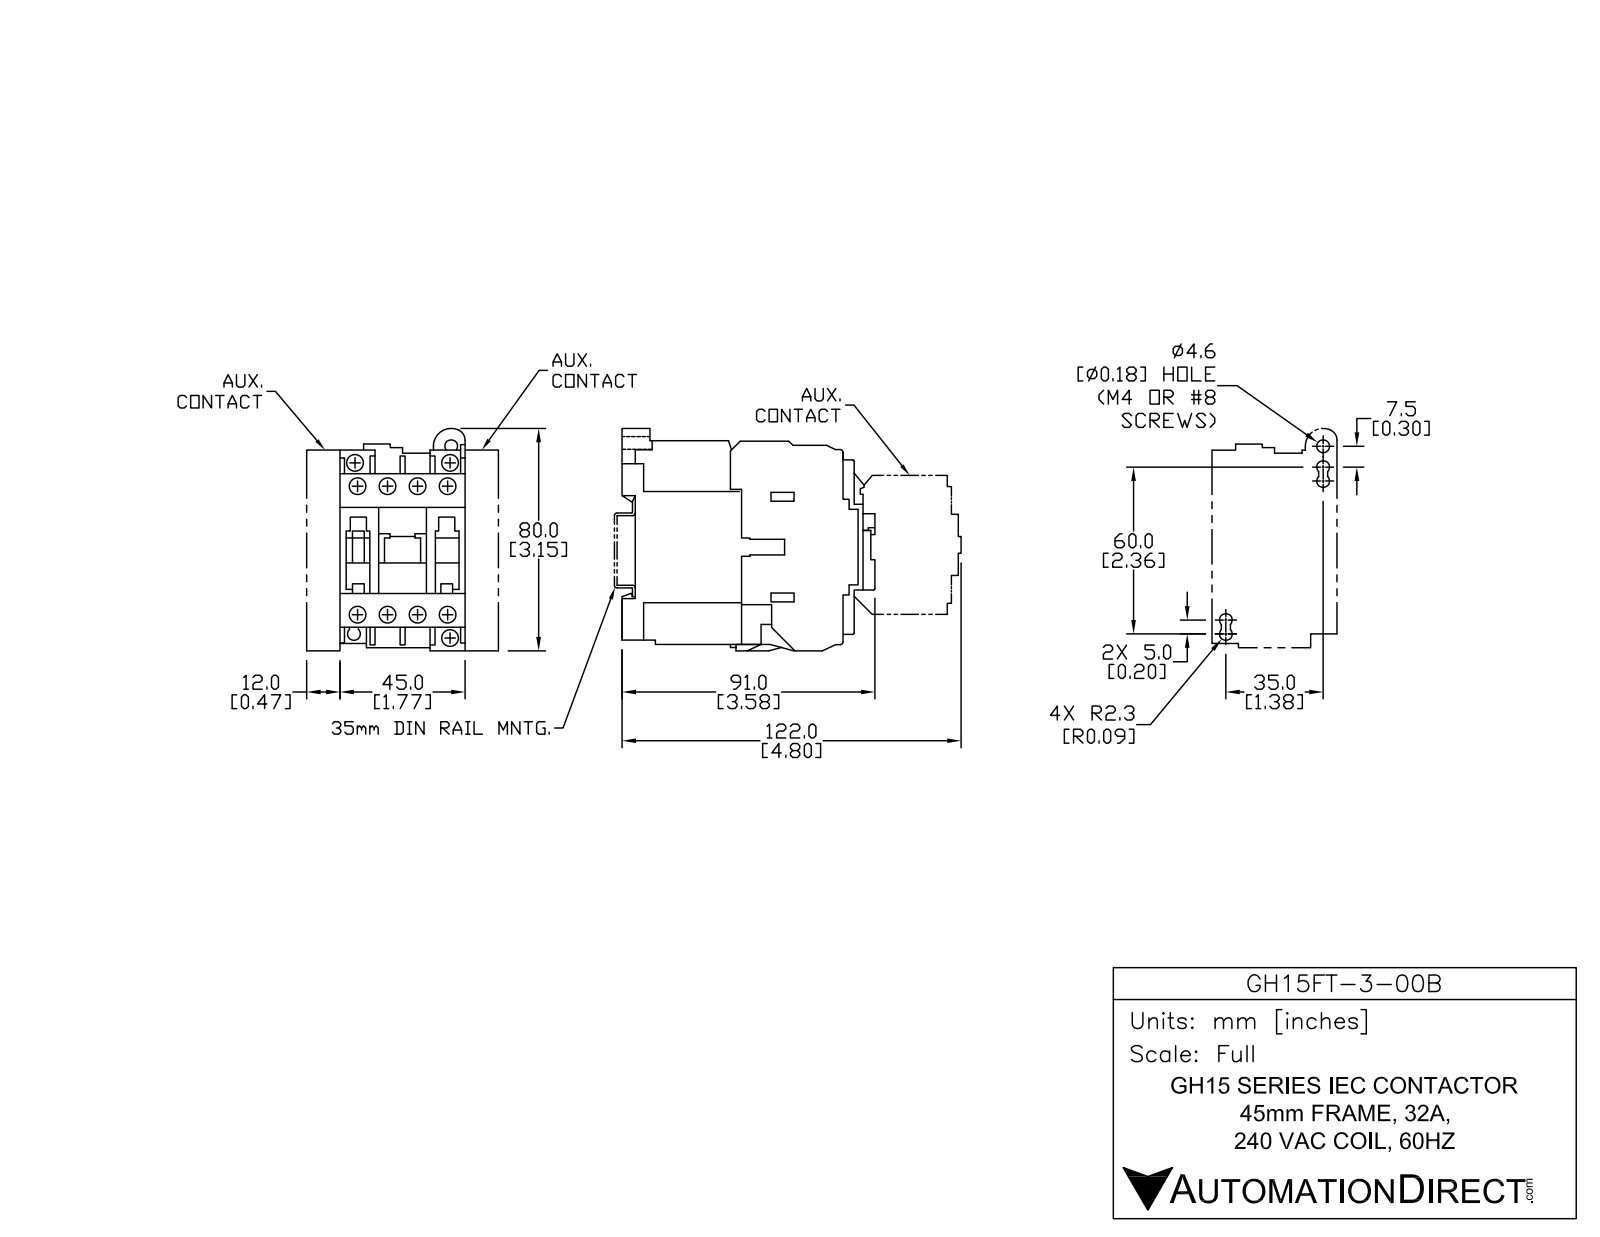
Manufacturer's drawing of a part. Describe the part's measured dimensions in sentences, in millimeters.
The part is named "GH15FT-3-00B". Its 3-D file was written by "SolidWorks 2009 (AUTOMOTIVE_DESIGN)". It is 1 solid with 676 faces: 479 planar, 51 cylindrical and 146 other. Overall it measures 91.5 by 80 by 45 millimeters. Its volume is 218 392 cubic millimeters and its surface area 38 409 square millimeters. Round holes: 6 of diameter 7, 3 of diameter 6.25, 1 of diameter 4.6. Partial cylindrical surfaces (rounded edges, fillets, slot ends): 9 of radius 1, 8 of radius 2.3, 2 of radius 3, 1 of radius 4.99, 1 of radius 5. The main face-to-face distances are 45, 15, 7.75, 35.5, 14, 1, 9.5, 43.25, 54, 1.75. The hole center spacings are 14.5, 55.91, 54, 29, 61.29, 4.67, 5.04, 5.89.
